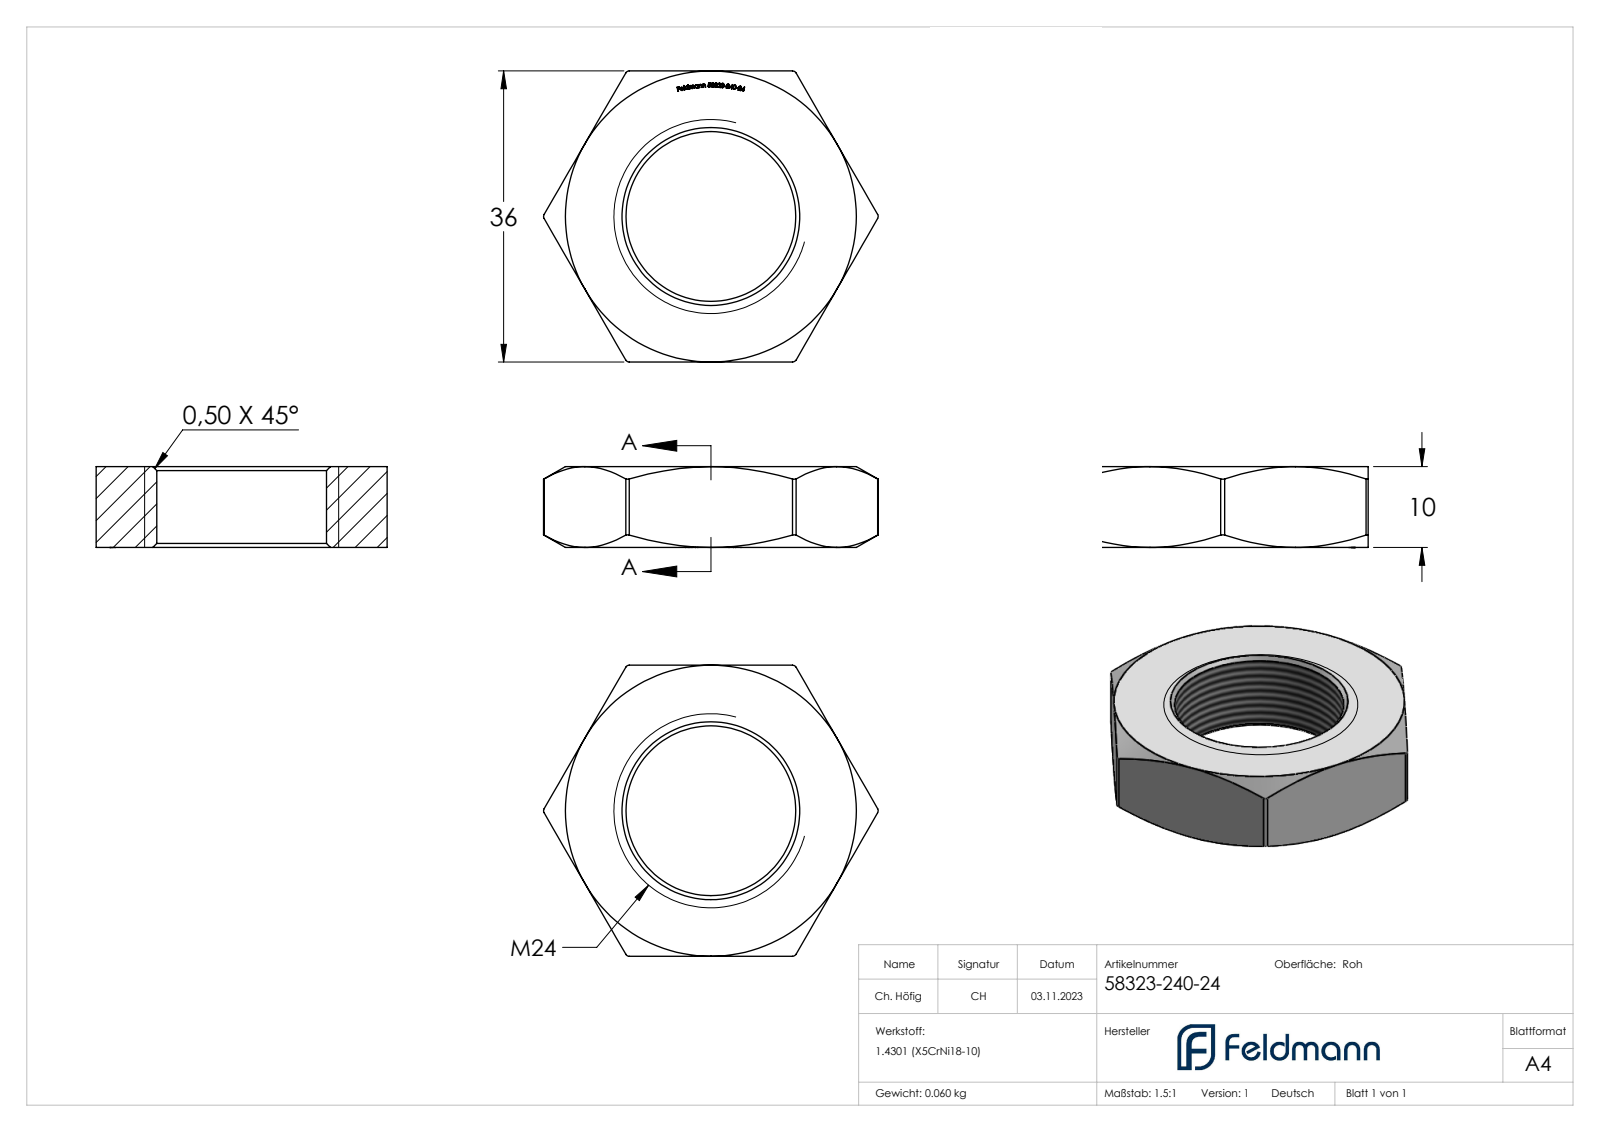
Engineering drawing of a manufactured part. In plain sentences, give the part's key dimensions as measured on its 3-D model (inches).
The part is named "58323-240-24". Its 3-D file was written by "SolidWorks 2018 (CONFIG_CONTROL_DESIGN)". It is 1 solid with 303 faces: 154 planar, 7 cylindrical and 142 other. Overall it measures 1.63 by 1.417 by 0.394 inches. Its volume is 0.466 cubic inches and its surface area 5.143 square inches. Round holes: 1 of diameter 0.827. Partial cylindrical surfaces (rounded edges, fillets, slot ends): 6 of radius 0.02. The main face-to-face distances are 0.394, 1.417, 0.39, 0.021, 0.019, 0.021, 0.012, 0.117, 0.115, 0.023.
